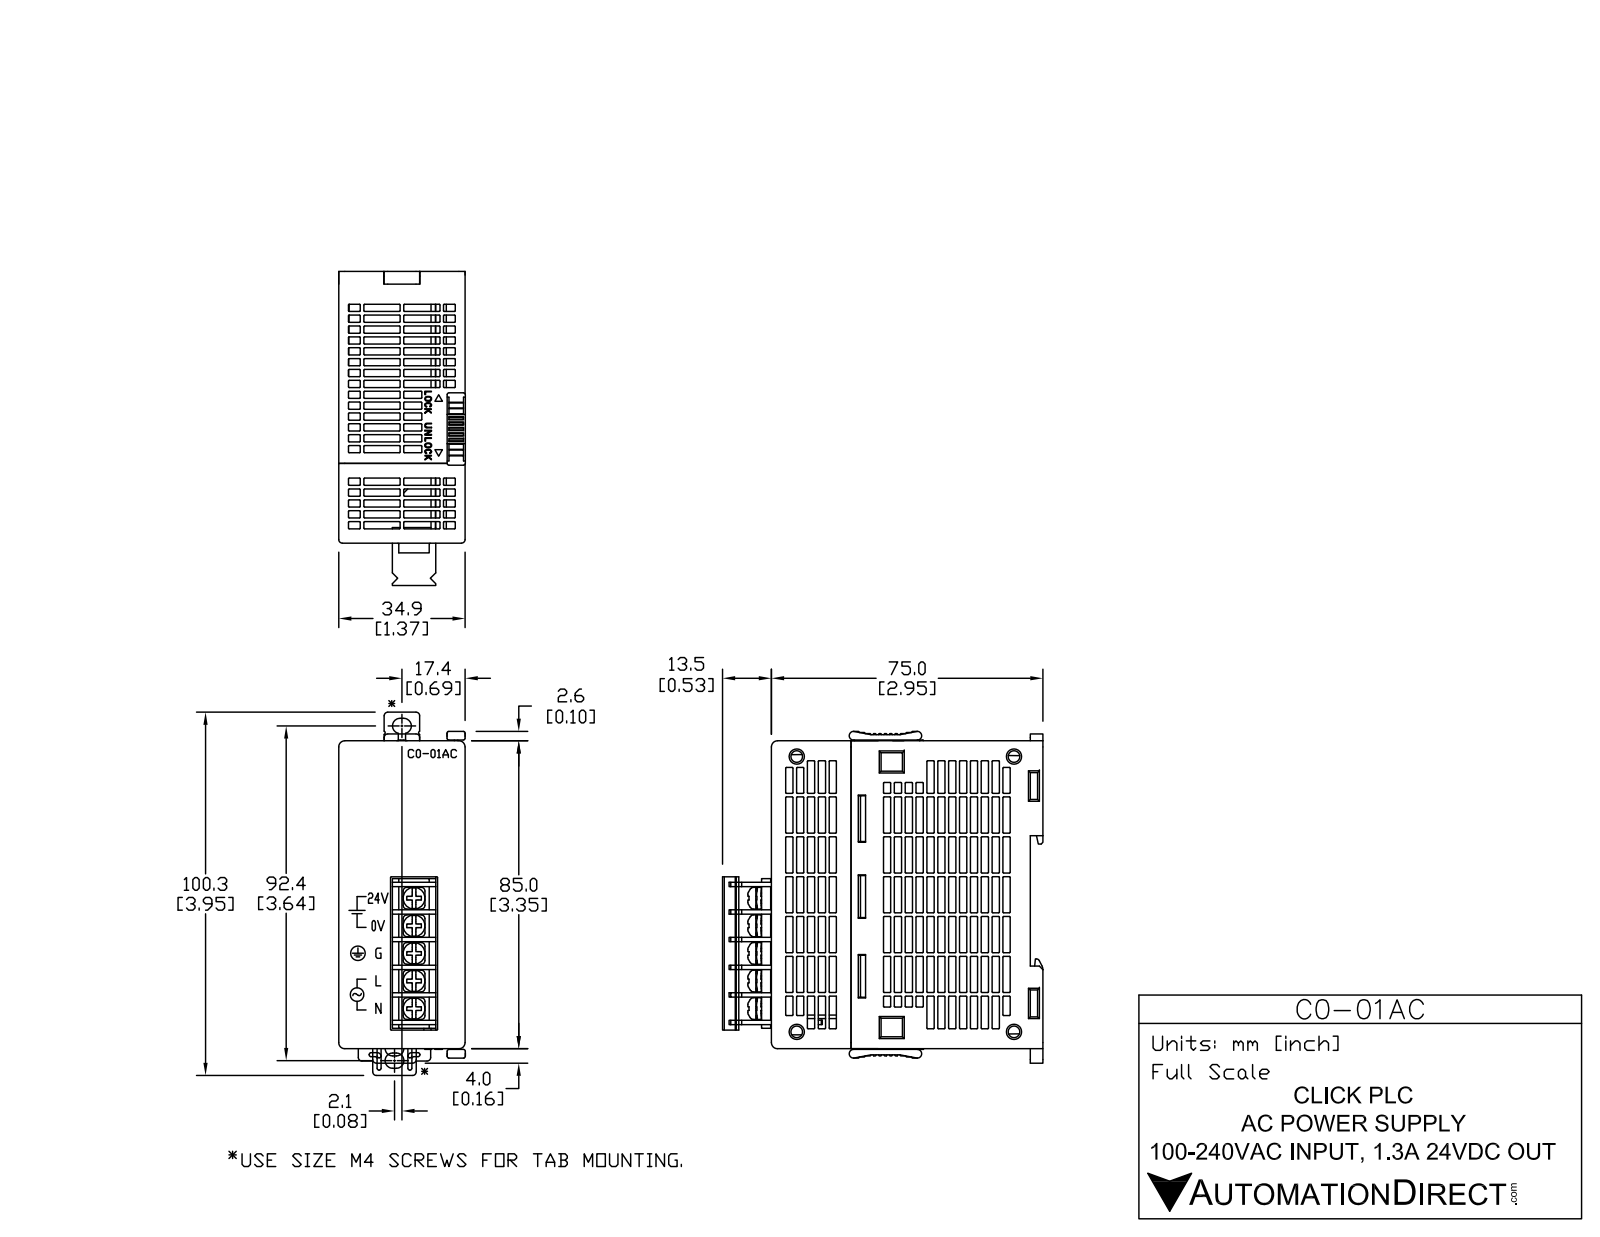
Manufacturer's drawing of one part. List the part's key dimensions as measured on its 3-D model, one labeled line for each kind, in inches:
Part name (STEP PRODUCT): C0-01AC
STEP written by: SolidWorks 2009 (AUTOMOTIVE_DESIGN)
Units: inches
Bodies: 1 solid, 4869 faces (3150 planar, 1599 cylindrical, 120 other)
Overall size (bounding box): 3.606 × 3.413 × 1.376
Volume: 13.09 in³ · Surface area: 51.44 in²
Round holes (diameter × count): ⌀0.079 ×2
Round bosses / shafts (diameter × count): ⌀0.236 ×5, ⌀0.118 ×5, ⌀0.075 ×1
Partial cylindrical surfaces — rounded edges, fillets, slot ends (radius × count): R0.008 ×820, R0.039 ×32, R0.02 ×30, R0.012 ×10, R0.067 ×6, R0.004 ×5, R0.047 ×4, R0.059 ×4
Main face-to-face distances: 0.02, 1.354, 1.374, 2.815, 3.327, 1.335, 3.346, 1.362, 1.343, 0.138
Hole centre spacings: 0.545
